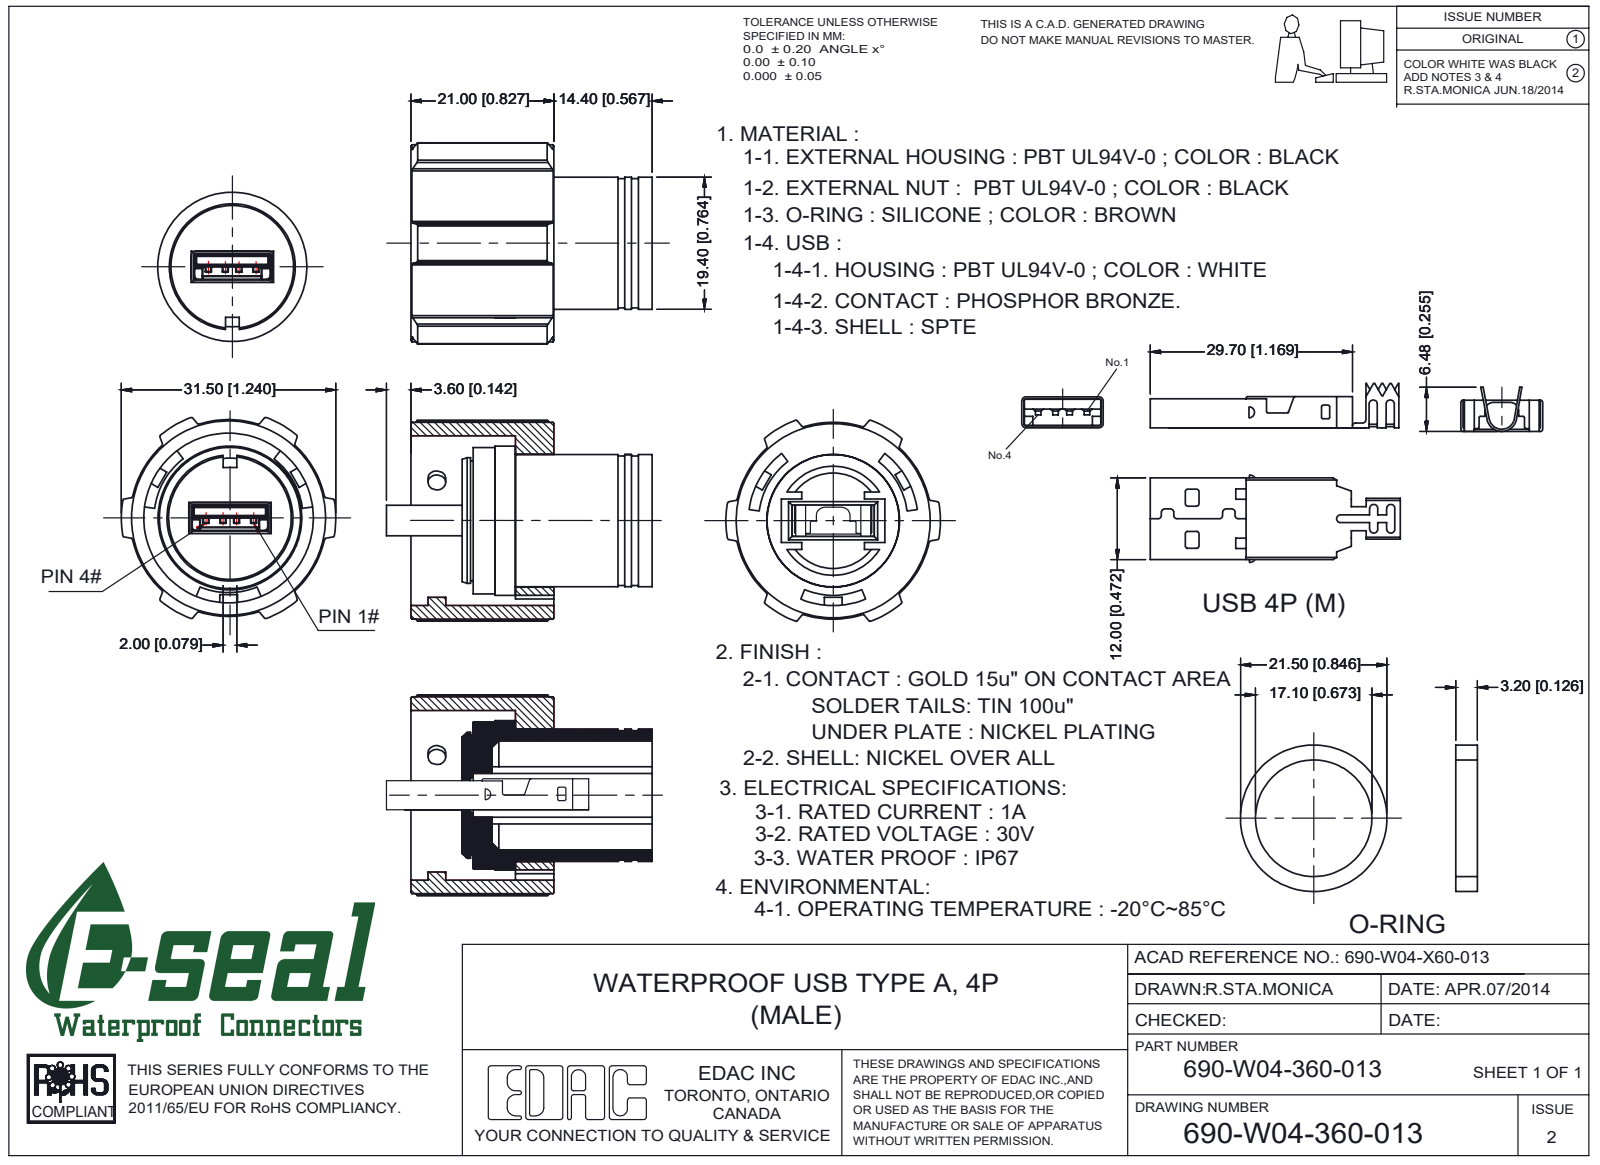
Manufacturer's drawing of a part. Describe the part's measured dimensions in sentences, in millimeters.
The part is named "HOUSING OUTER 690-W04-X60-013; CONTACTS 690-W04-X60-013; 690-W04-260-013; USB ASSY 690-W04-X60-013 (+6 more)". Its 3-D file was written by "SolidWorks 2020 (AUTOMOTIVE_DESIGN)". It is 10 solids with 980 faces: 670 planar, 282 cylindrical and 28 other. Overall it measures 40.51 by 31.5 by 29.5 millimeters. Its volume is 10 060 cubic millimeters and its surface area 12 995 square millimeters. Round holes: 1 of diameter 17.1, 1 of diameter 19.5, 1 of diameter 24.9. Round bosses or shafts: 1 of diameter 21.9, 1 of diameter 21.5, 1 of diameter 19.4, 1 of diameter 19, 1 of diameter 18.5, 1 of diameter 17.6. Partial cylindrical surfaces (rounded edges, fillets, slot ends): 62 of radius 0.2, 54 of radius 0.3, 11 of radius 0.5, 10 of radius 0.6, 8 of radius 0.25, 6 of radius 0.17, 4 of radius 0.28, 4 of radius 0.32. The main face-to-face distances are 4.2, 5.45, 1.25, 5.15, 0.95, 3, 3.9, 4.5, 1, 8.65.
